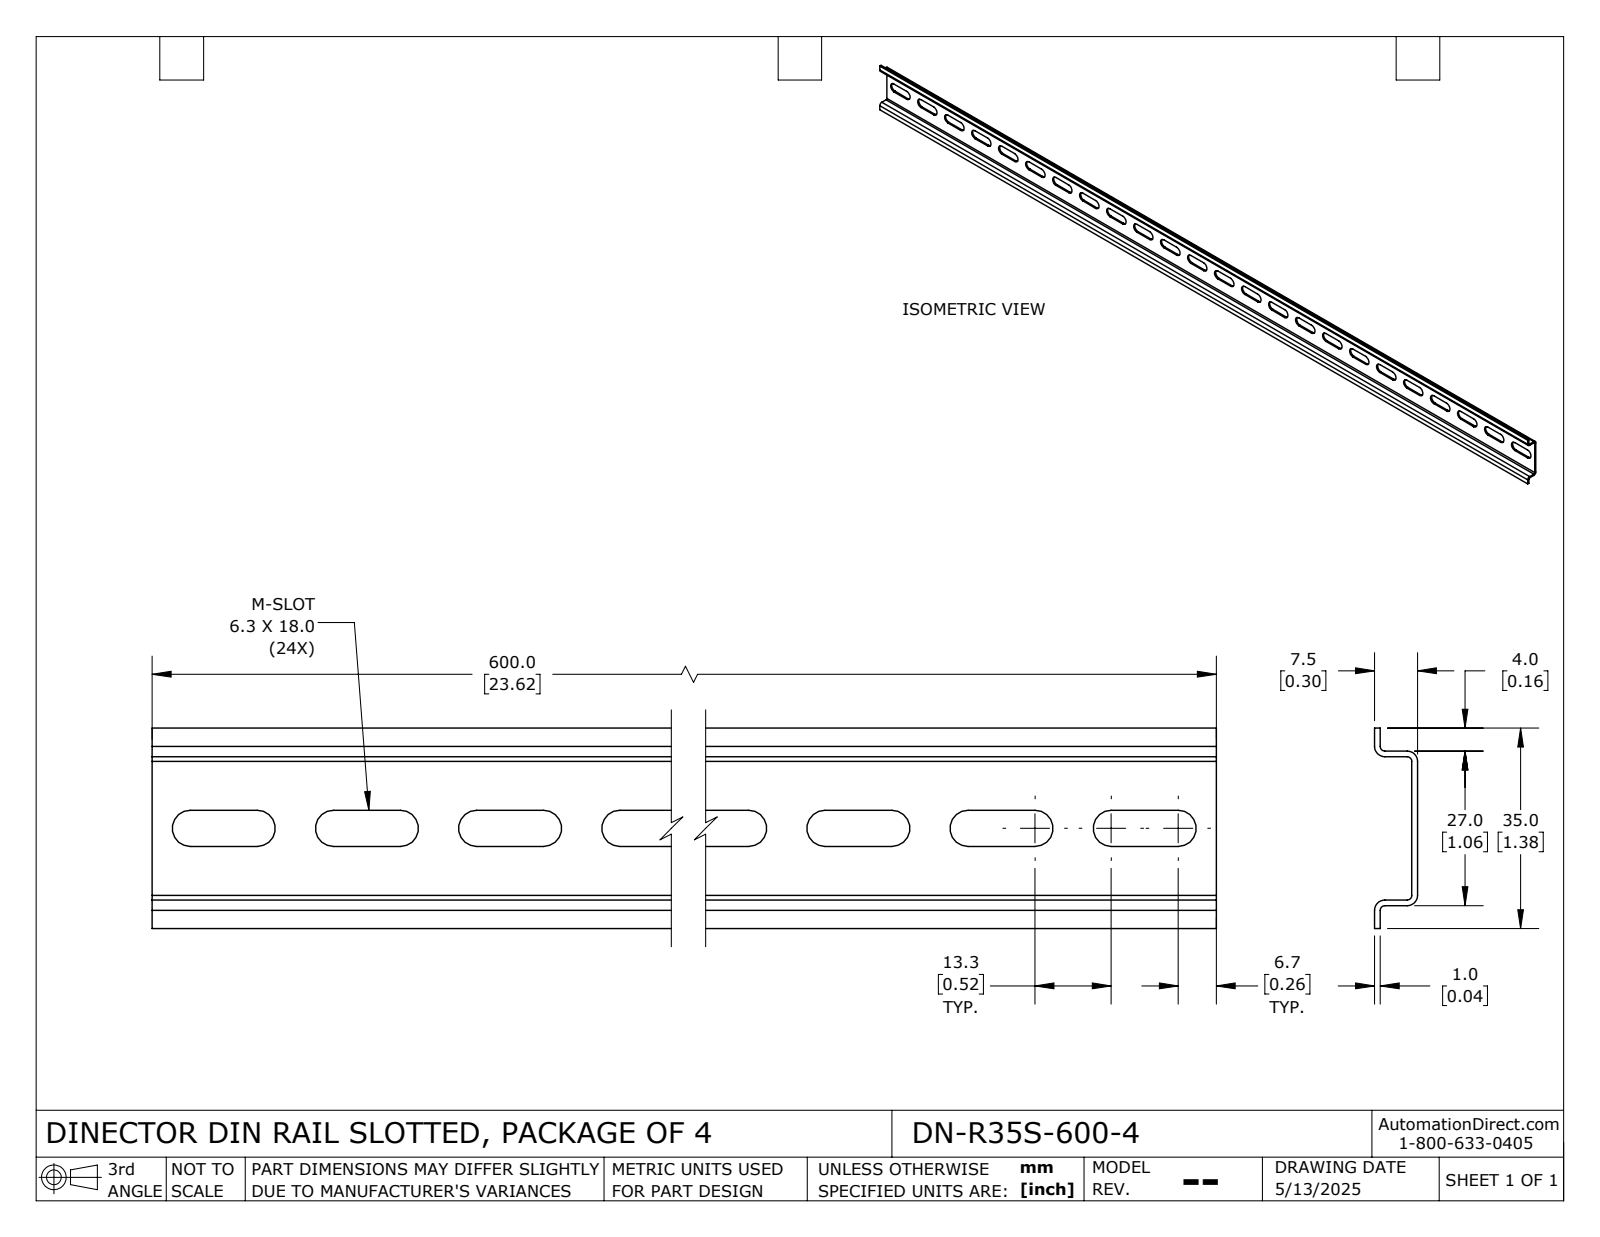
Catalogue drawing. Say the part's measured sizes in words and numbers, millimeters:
The part is named "DN-R35S-600-4_Default". Its 3-D file was written by "SolidWorks 2024 (CONFIG_CONTROL_DESIGN)". It is 1 solid with 118 faces: 62 planar, 56 cylindrical and 0 other. Overall it measures 600 by 35 by 7.5 millimeters. Its volume is 24 944 cubic millimeters and its surface area 52 216 square millimeters. Partial cylindrical surfaces (rounded edges, fillets, slot ends): 48 of radius 3.15, 4 of radius 0.8, 4 of radius 1.8. The main face-to-face distances are 1, 6.5, 26, 7.5, 5.5, 27, 25, 4, 5, 30.
